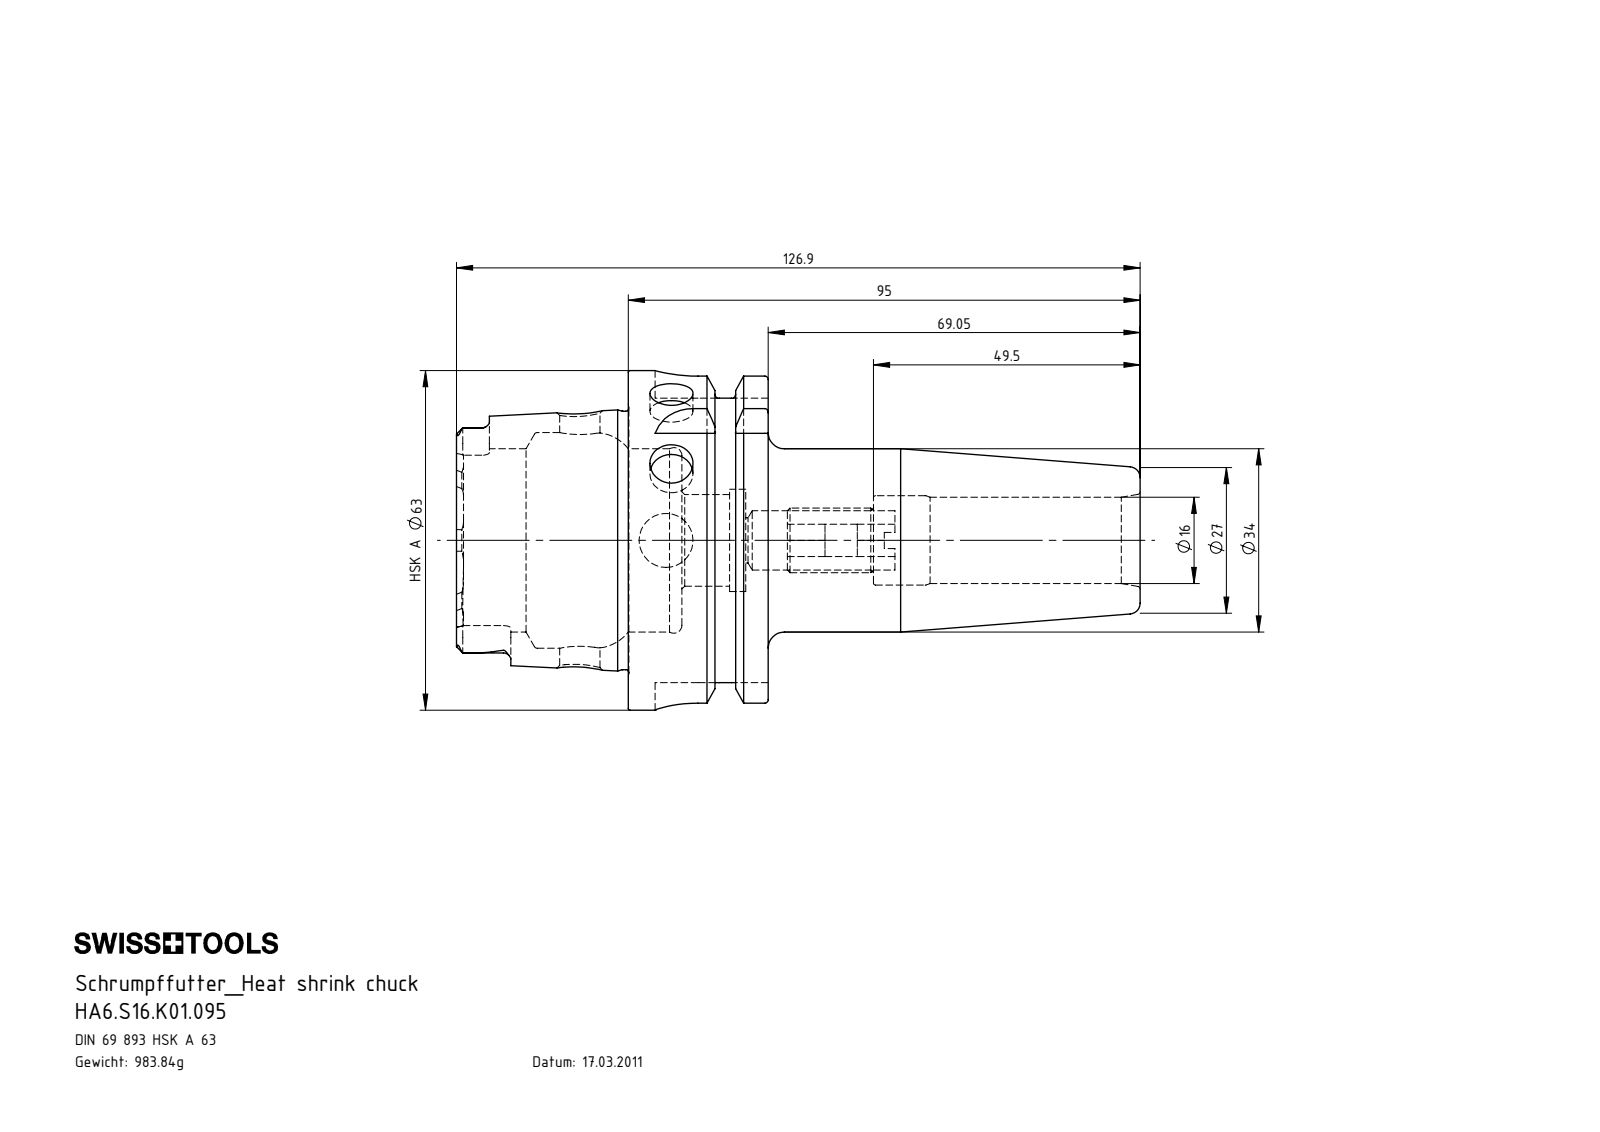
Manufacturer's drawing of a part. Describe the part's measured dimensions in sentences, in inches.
The part is named "HA6-S16.K01.095; ERU-AN5.K01.020_A; HA6-S16.K01.095_B_Fertigbearbeitung". Its 3-D file was written by "SolidWorks 2012 (AUTOMOTIVE_DESIGN)". It is 2 solids with 236 faces: 82 planar, 61 cylindrical and 93 other. Overall it measures 4.996 by 2.48 by 2.48 inches. Its volume is 7.648 cubic inches and its surface area 51.51 square inches. Round holes: 2 of diameter 0.315, 1 of diameter 0.236, 1 of diameter 0.295, 1 of diameter 0.331, 1 of diameter 0.394, 1 of diameter 0.433, 1 of diameter 0.63, 1 of diameter 0.654, 1 of diameter 0.669, 1 of diameter 0.748, 1 of diameter 1.339, 1 of diameter 1.575. Round bosses or shafts: 1 of diameter 2.48, 1 of diameter 2.163, 1 of diameter 1.887, 1 of diameter 0.472. Partial cylindrical surfaces (rounded edges, fillets, slot ends): 6 of radius 0.055, 4 of radius 0.113, 4 of radius 0.315. The main face-to-face distances are 1.022, 0.63, 0.392, 1.256, 1.648, 2.278, 2.079, 0.858, 0.467, 2.114.
